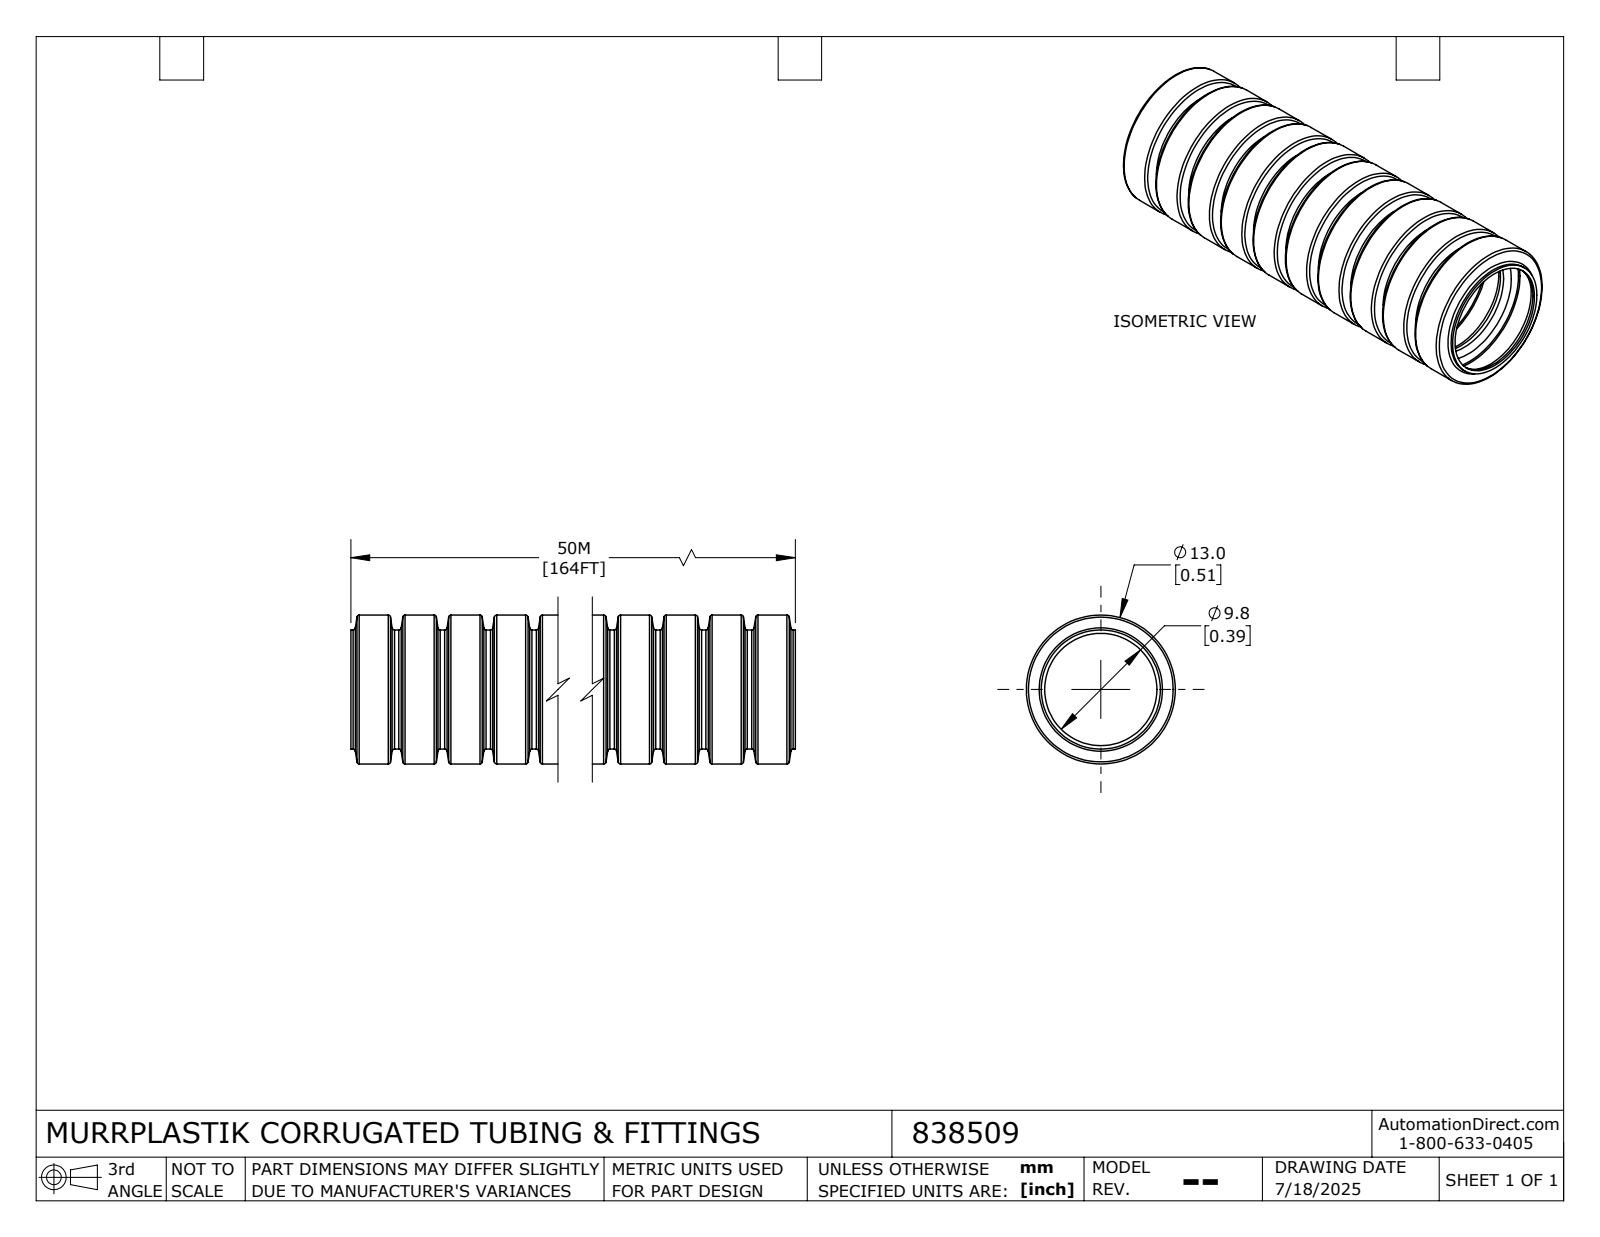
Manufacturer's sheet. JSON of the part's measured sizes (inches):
{"part_name": "838509_Default", "step_written_by": "SolidWorks 2024 (CONFIG_CONTROL_DESIGN)", "units": "inches", "bodies": {"solids": 1, "faces": 164, "planar": 2, "cylindrical": 42, "other": 120}, "overall_size": [1.575, 0.512, 0.512], "volume_in3": 0.041, "surface_area_in2": 6.834, "round_holes": [[0.386, 1], [0.488, 1]], "round_bosses_or_shafts": [[0.512, 1], [0.409, 1]], "face_to_face_distances": [1.575]}
